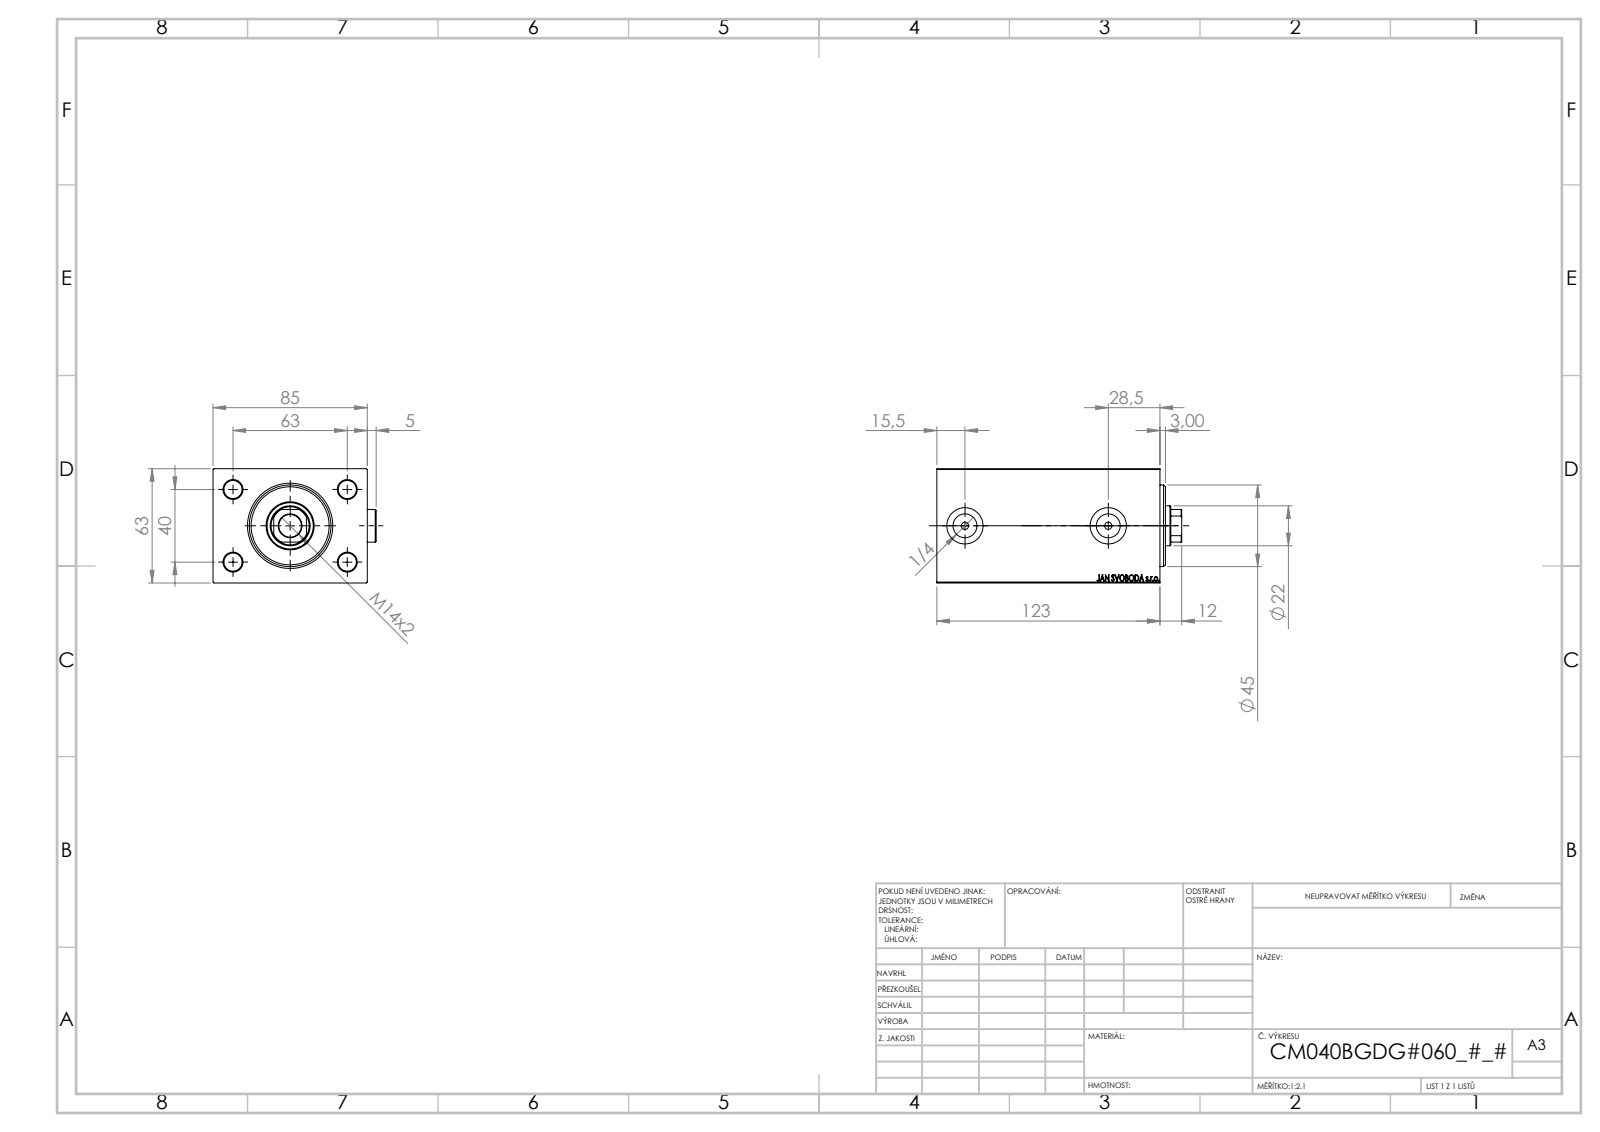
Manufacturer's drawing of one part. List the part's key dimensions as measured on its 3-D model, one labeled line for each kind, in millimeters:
Part name (STEP PRODUCT): Zatka_OIL_PORT; V450CM_B_Body; V450CM_VC_B; V450CM_B_VCP
STEP written by: SolidWorks 2019 (CONFIG_CONTROL_DESIGN)
Units: millimetres
Bodies: 5 solids, 935 faces (435 planar, 70 cylindrical, 430 other)
Overall size (bounding box): 135 × 89.9 × 63
Volume: 592 286 mm³ · Surface area: 89 758 mm²
Round holes (diameter × count): ⌀10 ×4, ⌀4 ×2, ⌀13.16 ×2, ⌀20 ×2, ⌀12.5 ×1, ⌀22 ×1, ⌀25.5 ×1, ⌀26.5 ×1, ⌀40 ×1, ⌀42 ×1, ⌀45 ×1
Round bosses / shafts (diameter × count): ⌀18 ×2
Partial cylindrical surfaces — rounded edges, fillets, slot ends (radius × count): R10.5 ×1
Main face-to-face distances: 63, 85, 12, 111, 123, 84.9, 99, 72, 3, 15
Hole centre spacings: 37.31, 40, 63, 74.63, 79
